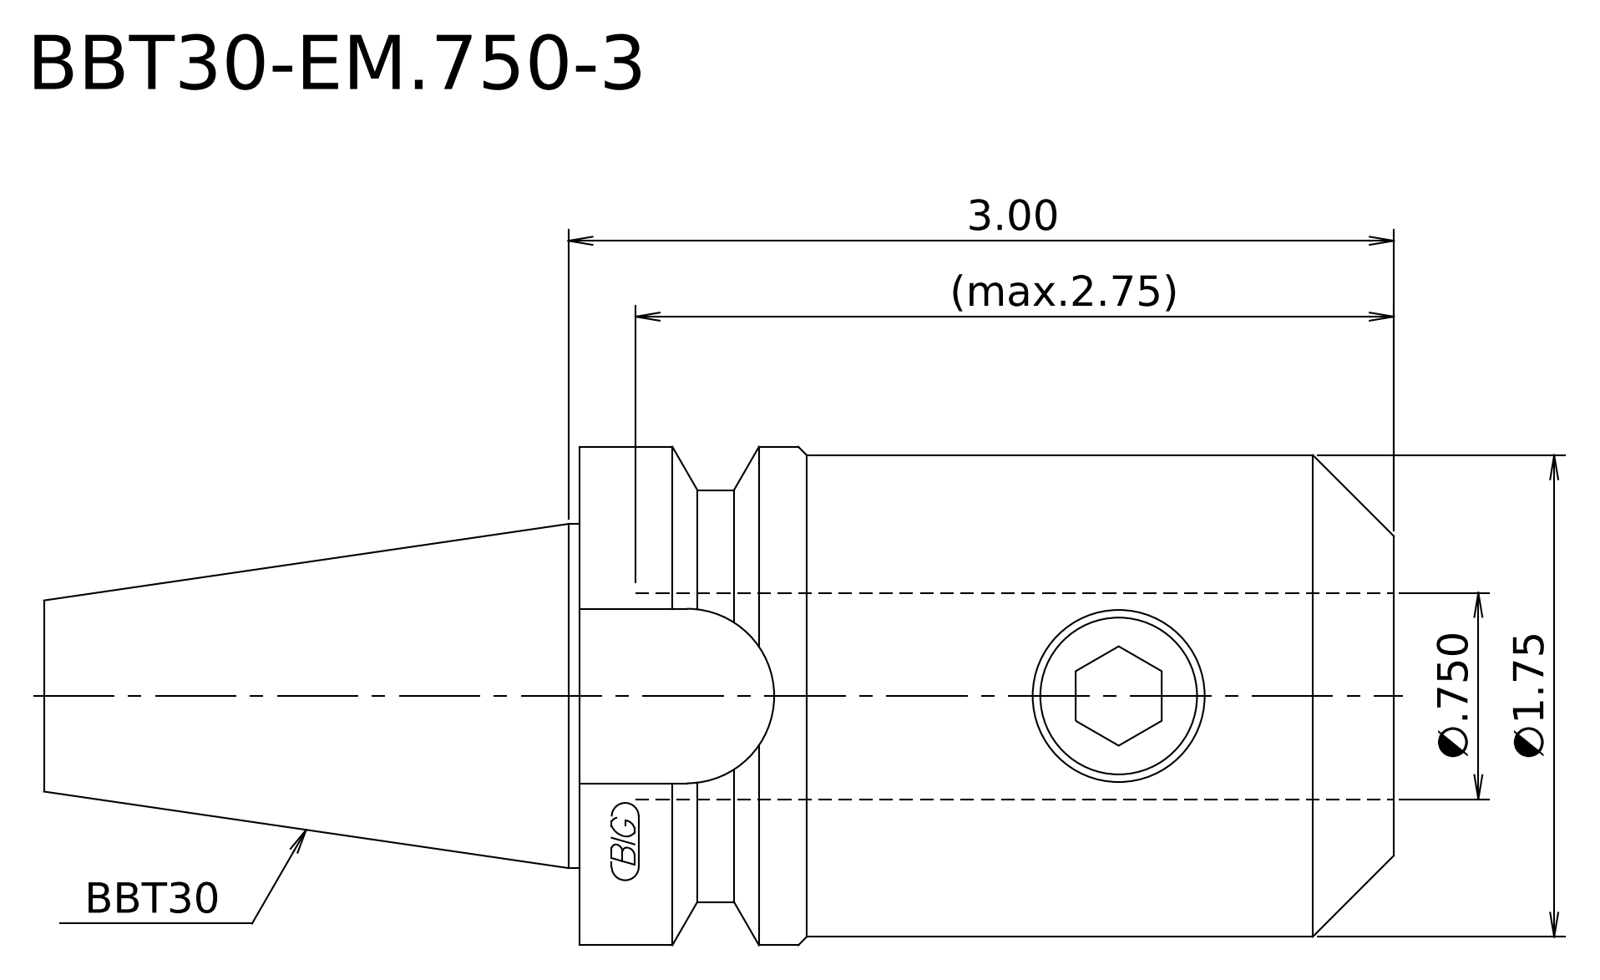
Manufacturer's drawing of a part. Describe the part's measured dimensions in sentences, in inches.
The part is named "BBT30-EM_750-3". Its 3-D file was written by "SolidWorks 2021 (CONFIG_CONTROL_DESIGN)". It is 1 solid with 27 faces: 7 planar, 12 cylindrical and 8 other. Overall it measures 4.906 by 1.811 by 1.811 inches. Its volume is 7.424 cubic inches and its surface area 31.77 square inches. Round holes: 1 of diameter 0.75. Round bosses or shafts: 1 of diameter 1.811, 1 of diameter 1.75, 1 of diameter 1.496, 1 of diameter 1.25. The main face-to-face distances are 2.98, 2.173, 0.807, 4.906, 2.732, 1.925, 2.366, 2.484, 0.193, 0.311.
